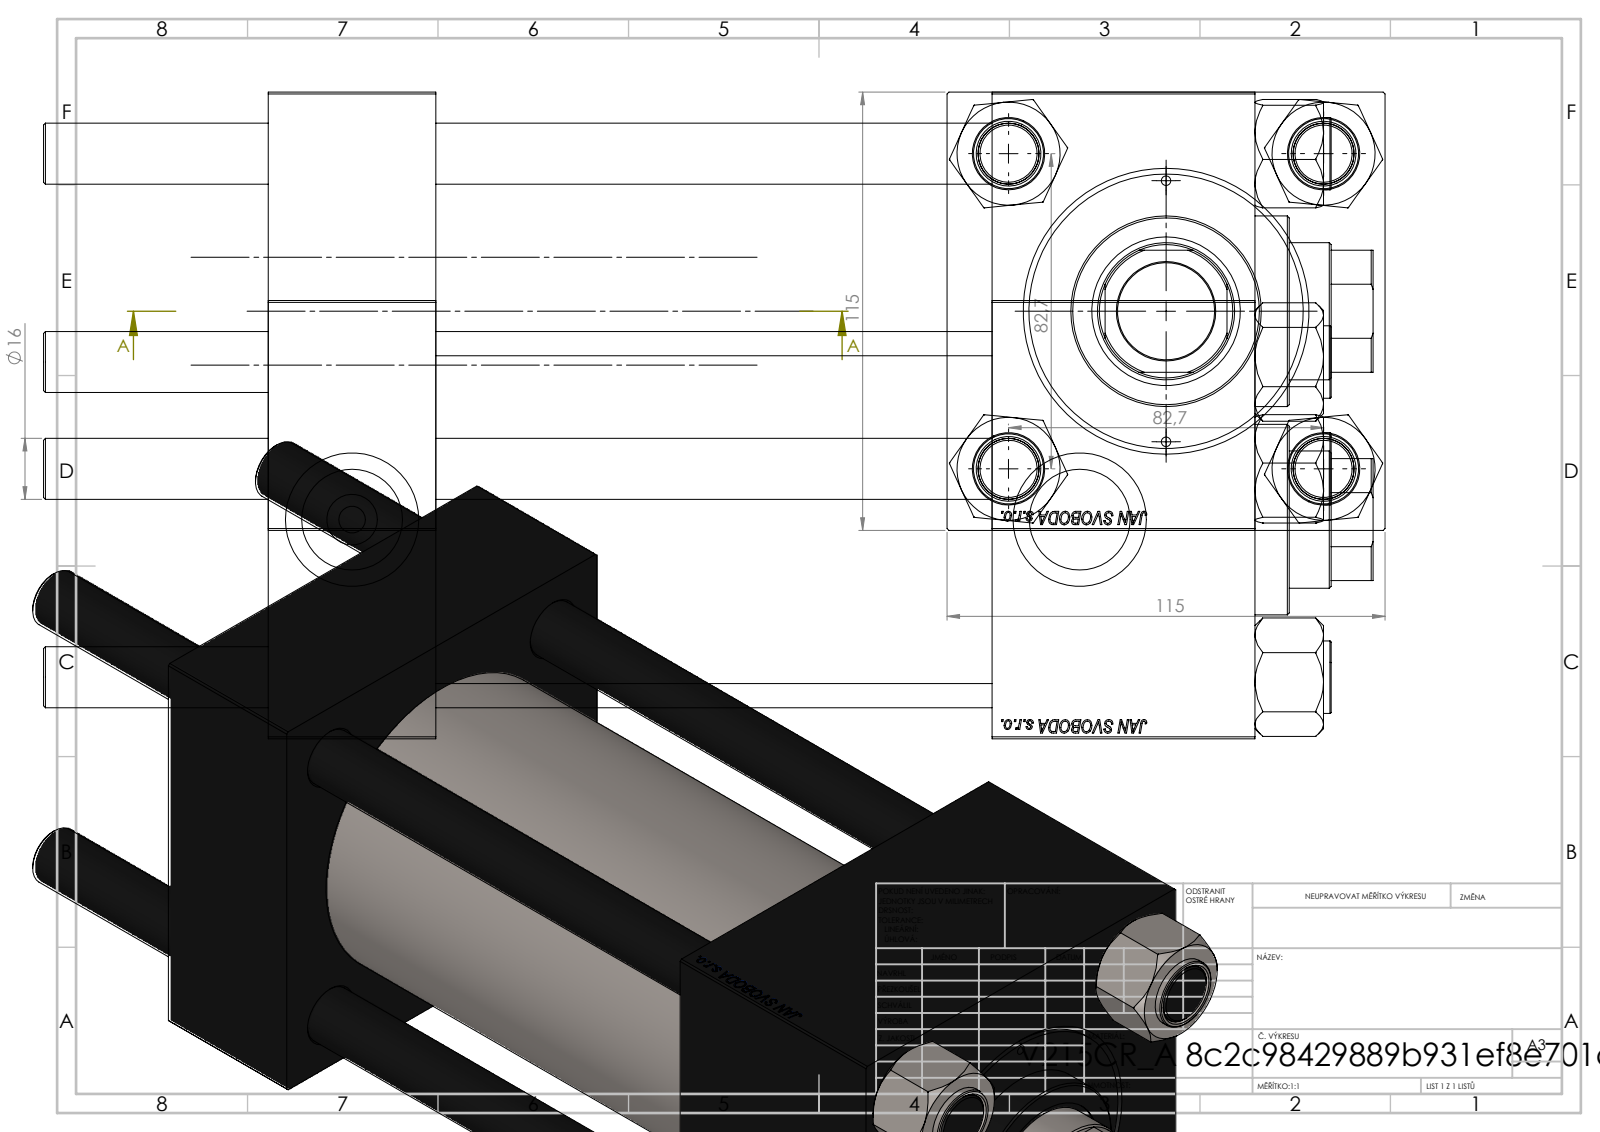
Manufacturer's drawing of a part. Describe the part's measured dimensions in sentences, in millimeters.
The part is named "V215CR_VCP; CR025_012_A_0_G_A_G_M_020_+#_##_TYCINKA; V215CR_BODY_A; NUT_M5 (+1 more)". Its 3-D file was written by "SolidWorks 2019 (CONFIG_CONTROL_DESIGN)". It is 11 solids with 1188 faces: 570 planar, 82 cylindrical and 536 other. Overall it measures 349 by 115 by 115 millimeters. Its volume is 2 074 000 cubic millimeters and its surface area 361 526 square millimeters. Round holes: 4 of diameter 16, 2 of diameter 2.5, 2 of diameter 7, 2 of diameter 26.44, 2 of diameter 35, 1 of diameter 25.5, 1 of diameter 36, 1 of diameter 39, 1 of diameter 61, 1 of diameter 72, 1 of diameter 80. Round bosses or shafts: 4 of diameter 19, 1 of diameter 86, 1 of diameter 50. Partial cylindrical surfaces (rounded edges, fillets, slot ends): 1 of radius 17.5. The main face-to-face distances are 115, 44, 259, 215, 69, 190, 146, 100, 230.3, 186.3. The hole center spacings are 41.96, 58.48, 82.7, 86.17, 34.25, 116.96, 68.5, 191.
